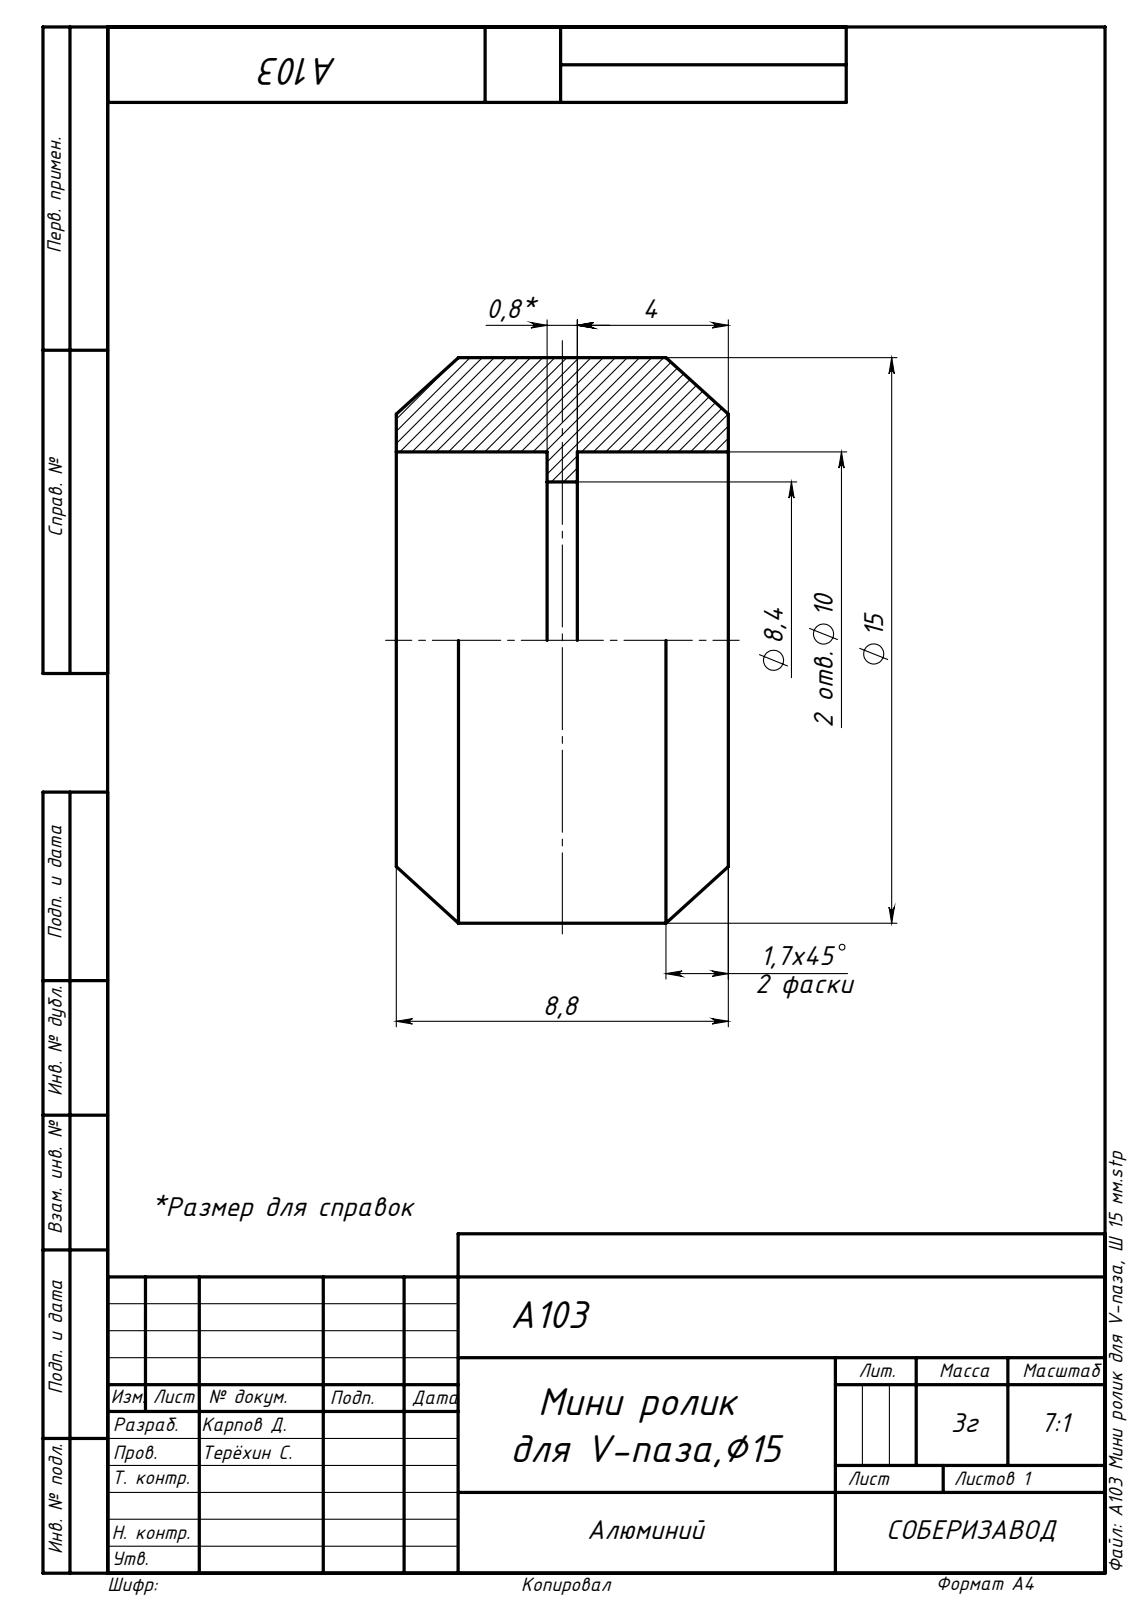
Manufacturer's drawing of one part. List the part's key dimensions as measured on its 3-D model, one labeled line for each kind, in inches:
Part name (STEP PRODUCT): A180
STEP written by: Autodesk Inventor 2018 (AP242_MANAGED_MODEL_BASED_3D_ENGINEERING_MIM_LF)
Units: inches
Bodies: 1 solid, 10 faces (4 planar, 4 cylindrical, 2 other)
Overall size (bounding box): 0.591 × 0.591 × 0.346
Volume: 0.047 in³ · Surface area: 1.3 in²
Round holes (diameter × count): ⌀0.331 ×1, ⌀0.394 ×1
Round bosses / shafts (diameter × count): ⌀0.591 ×1
Main face-to-face distances: 0.157, 0.189, 0.346, 0.031
